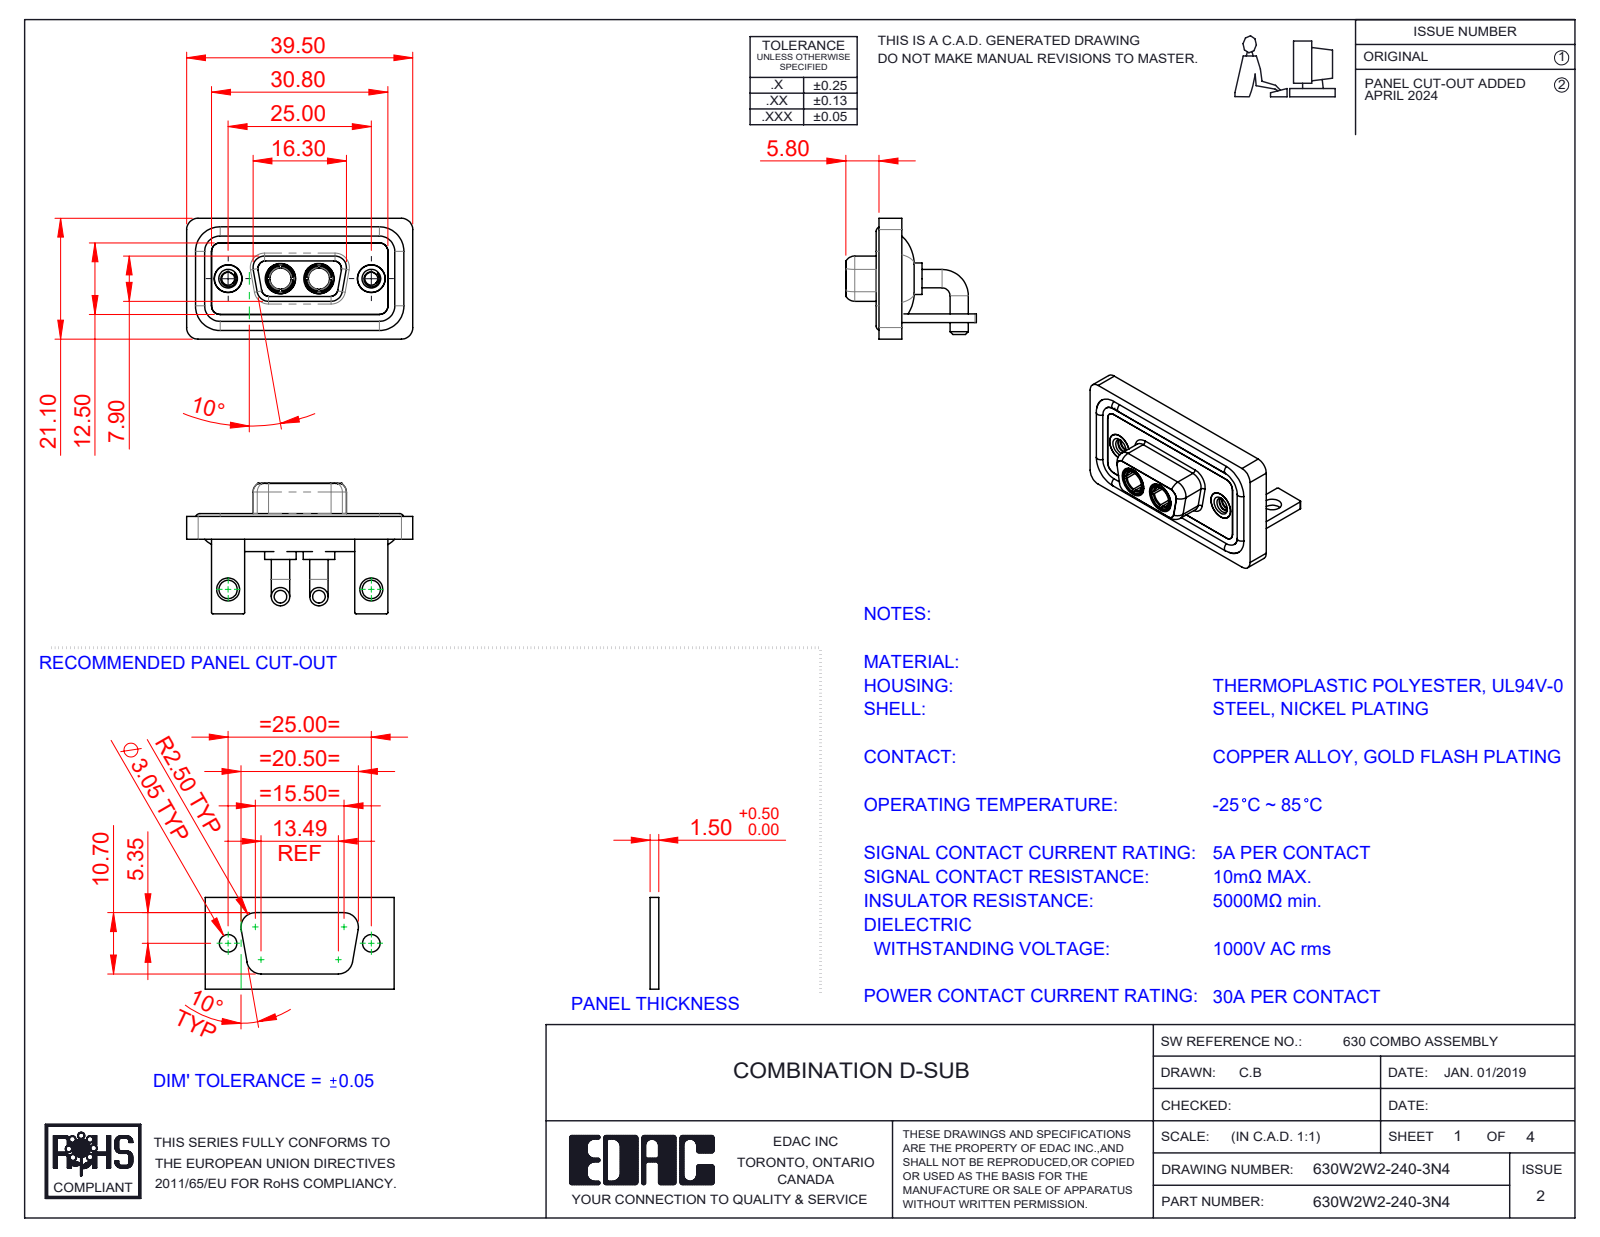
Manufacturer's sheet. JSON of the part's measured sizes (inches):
{"part_name": "630Combo Waterproof Housing_09 Contacts; Power Socket_30A RA; 630W2W2-140-3N4; 630Combo Shell Front_09 Contacts (+4 more)", "step_written_by": "SolidWorks 2023 (CONFIG_CONTROL_DESIGN)", "units": "inches", "bodies": {"solids": 13, "faces": 590, "planar": 183, "cylindrical": 262, "other": 145}, "overall_size": [1.555, 0.898, 0.831], "volume_in3": 0.32, "surface_area_in2": 13.26, "round_holes": [[0.191, 4], [0.089, 2], [0.126, 2], [0.146, 2], [0.157, 2], [0.159, 2], [0.197, 2], [0.209, 2]], "round_bosses_or_shafts": [[0.126, 4], [0.063, 4], [0.217, 2], [0.205, 2], [0.195, 2], [0.195, 2], [0.189, 2], [0.187, 2]], "partial_cylinders_radius": [[0.079, 19], [0.059, 18], [0.01, 16], [0.053, 8], [0.063, 8], [0.02, 5], [0.024, 4], [0.026, 4]], "face_to_face_distances": [0.016, 0.114, 0.059, 0.071, 0.043, 0.146, 0.031, 0.098, 0.063, 0.122], "hole_center_spacings": [0.36, 0.624, 0.984, 0.265]}
